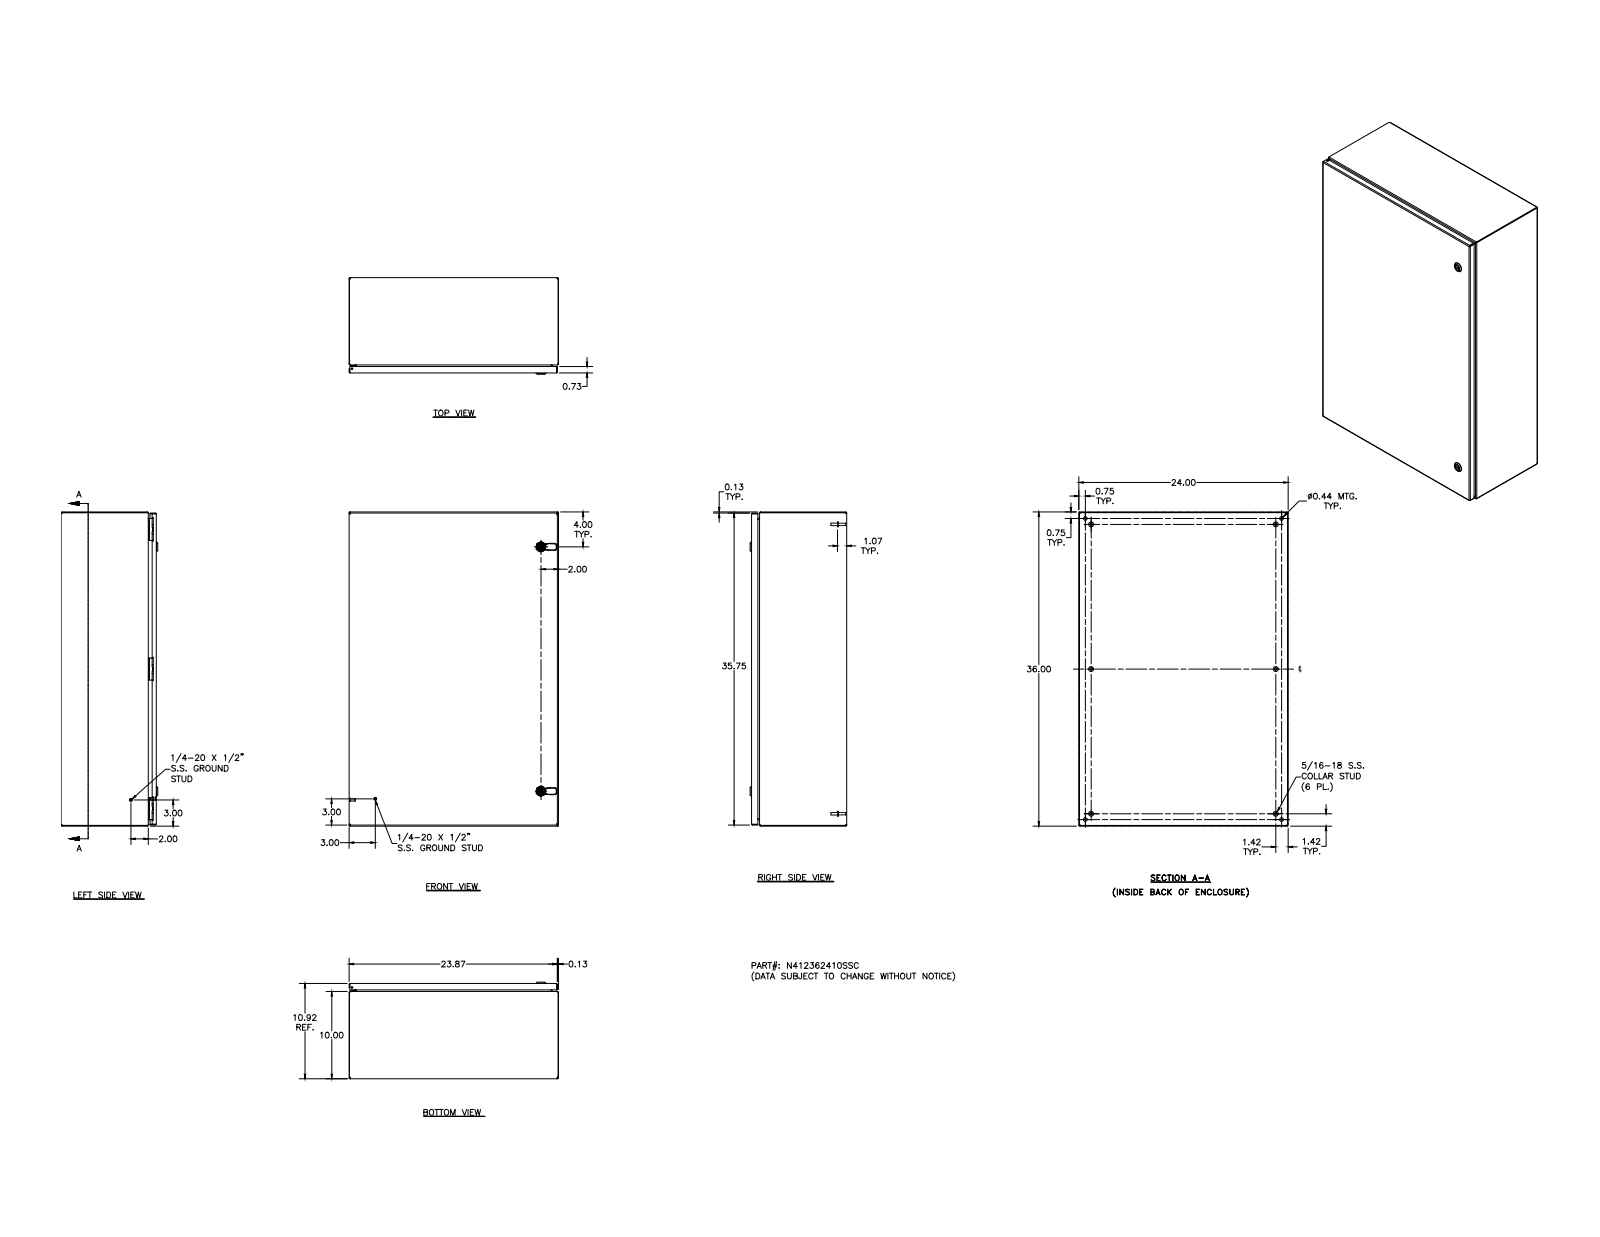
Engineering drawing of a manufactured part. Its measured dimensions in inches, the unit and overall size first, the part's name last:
Units: inches
Overall size (bounding box): 36 × 24 × 11.075
Round holes (diameter × count): ⌀0.188 ×7, ⌀0.093 ×6, ⌀0.152 ×6, ⌀0.167 ×6, ⌀0.172 ×6, ⌀0.437 ×4, ⌀0.156 ×3, ⌀0.197 ×2, ⌀0.315 ×2, ⌀0.394 ×2, ⌀0.402 ×2, ⌀0.634 ×2
Round bosses / shafts (diameter × count): ⌀0.25 ×14, ⌀0.563 ×6, ⌀0.36 ×6, ⌀0.32 ×6, ⌀0.3 ×6, ⌀0.275 ×6, ⌀0.256 ×6, ⌀0.164 ×6
Partial cylindrical surfaces — rounded edges, fillets, slot ends (radius × count): R0.05 ×38, R0.031 ×34, R0.016 ×26, R0.125 ×21, R0.105 ×20, R0.02 ×15, R0.032 ×12, R0.07 ×8
Main face-to-face distances: 0.074, 10.843, 10.769, 10.917, 23.926, 35.926, 23.852, 24, 35.852, 36
Hole centre spacings: 16.004, 32, 15.996, 0.017, 0.66, 15.992, 16, 16.008
Volume: 235.4 in³ · Surface area: 6 388 in²
Bodies: 53 solids, 2118 faces (831 planar, 778 cylindrical, 509 other)
Part name (STEP PRODUCT): N412362410SSC; N412362410SSCBKP; 388151; N4123624SSCLID (+8 more)
STEP written by: Autodesk Inventor 2011 (AUTOMOTIVE_DESIGN)
